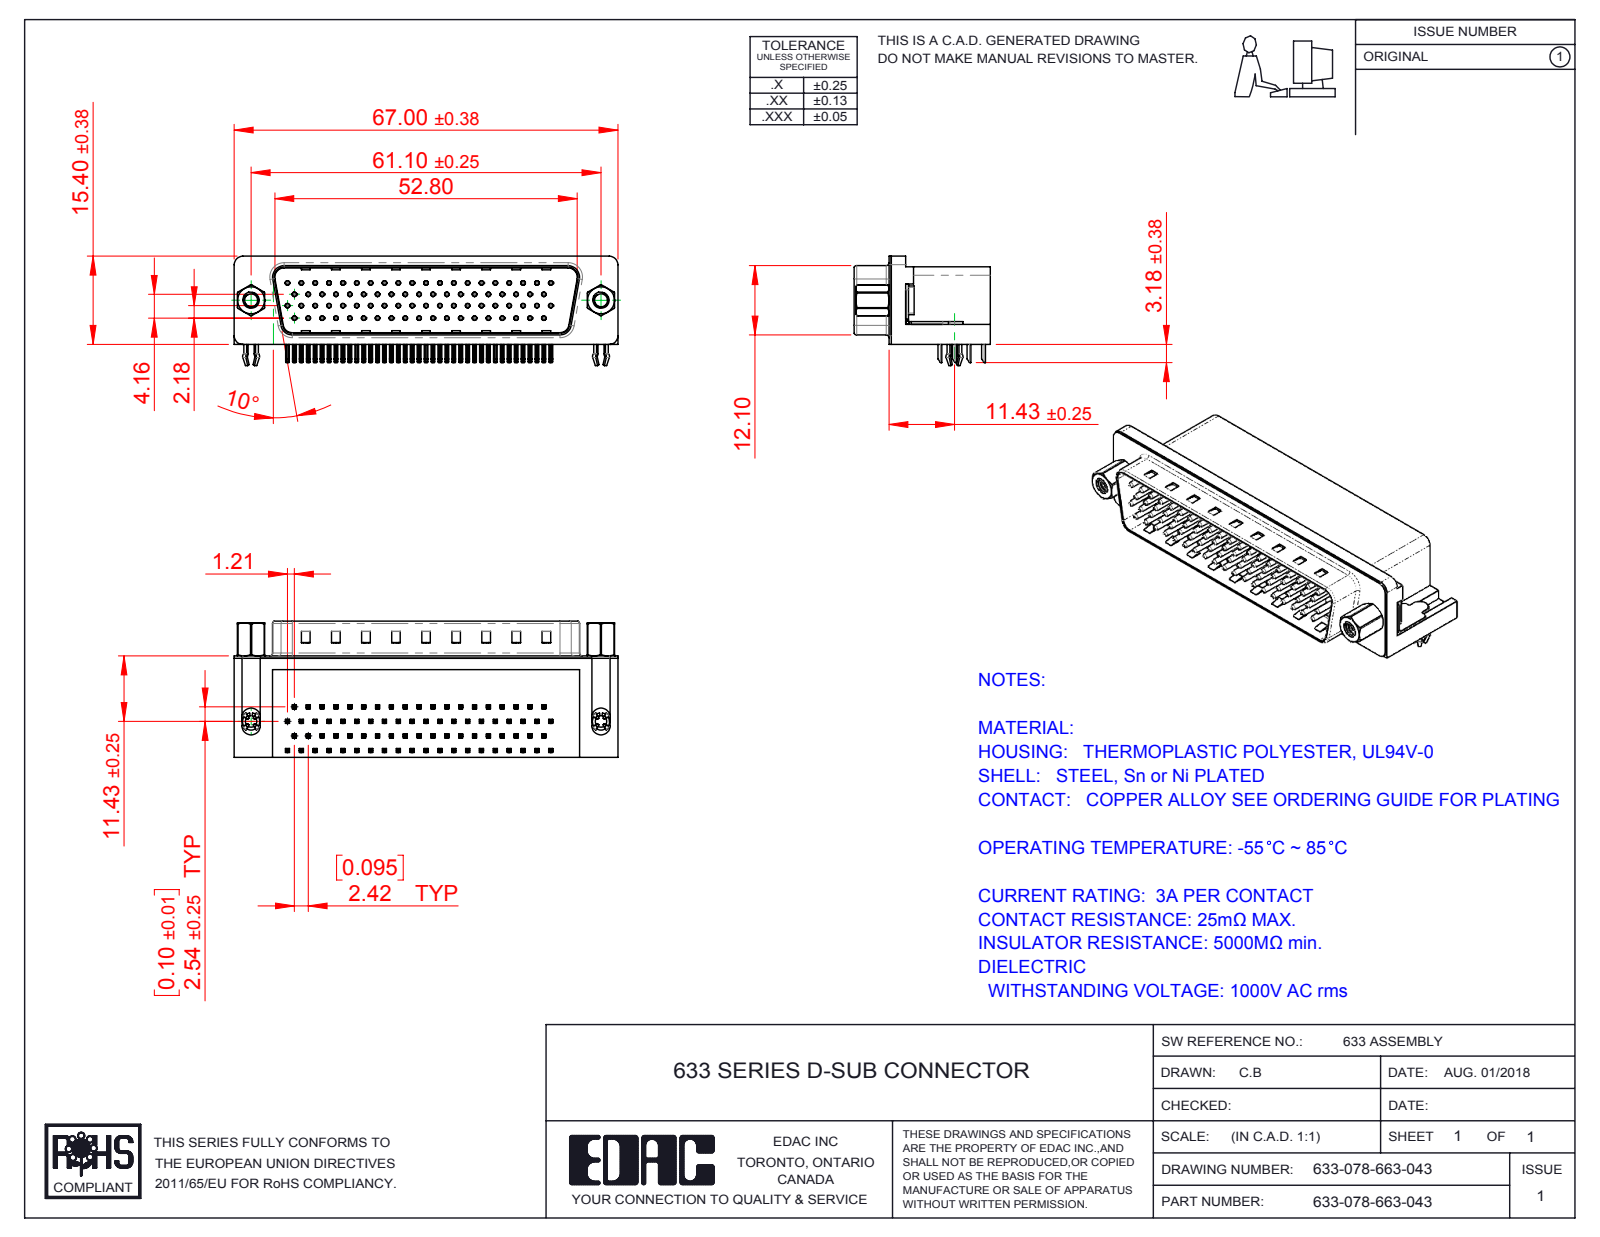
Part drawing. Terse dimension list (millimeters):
name: 633 4-40 Threaded Rivet; 633-078-663-043; 633 4 Prong Board Lock_78 Contact; 633 Contact Top_78 Contact (+6 more)
written by: SolidWorks 2016 (CONFIG_CONTROL_DESIGN)
unit: mm
bodies: 86 solids, 6516 faces (4045 planar, 1848 cylindrical, 623 other)
size: 67 × 23.8 × 19.1
volume: 14 825 mm³; area: 16 882 mm²
holes: 78× ⌀0.35, 78× ⌀0.8, 2× ⌀2, 2× ⌀2.26, 2× ⌀2.29, 2× ⌀4, 2× ⌀4.8, 2× ⌀5
bosses: 78× ⌀0.75, 2× ⌀4.9, 2× ⌀4.75, 2× ⌀3.9, 2× ⌀3, 2× ⌀2.79
rounds: 324× R0.25, 156× R0.12, 16× R1, 9× R0.5, 8× R1.6, 6× R1.5, 4× R0.45, 4× R0.9
face distances: 0.4, 13.2, 17.3, 11.7, 13.35, 2.05, 13.75, 1.65, 1.85, 11.9
hole spacings: 2.42, 4.84, 7.26, 9.68, 6.26, 7.13, 12.1, 8.62
